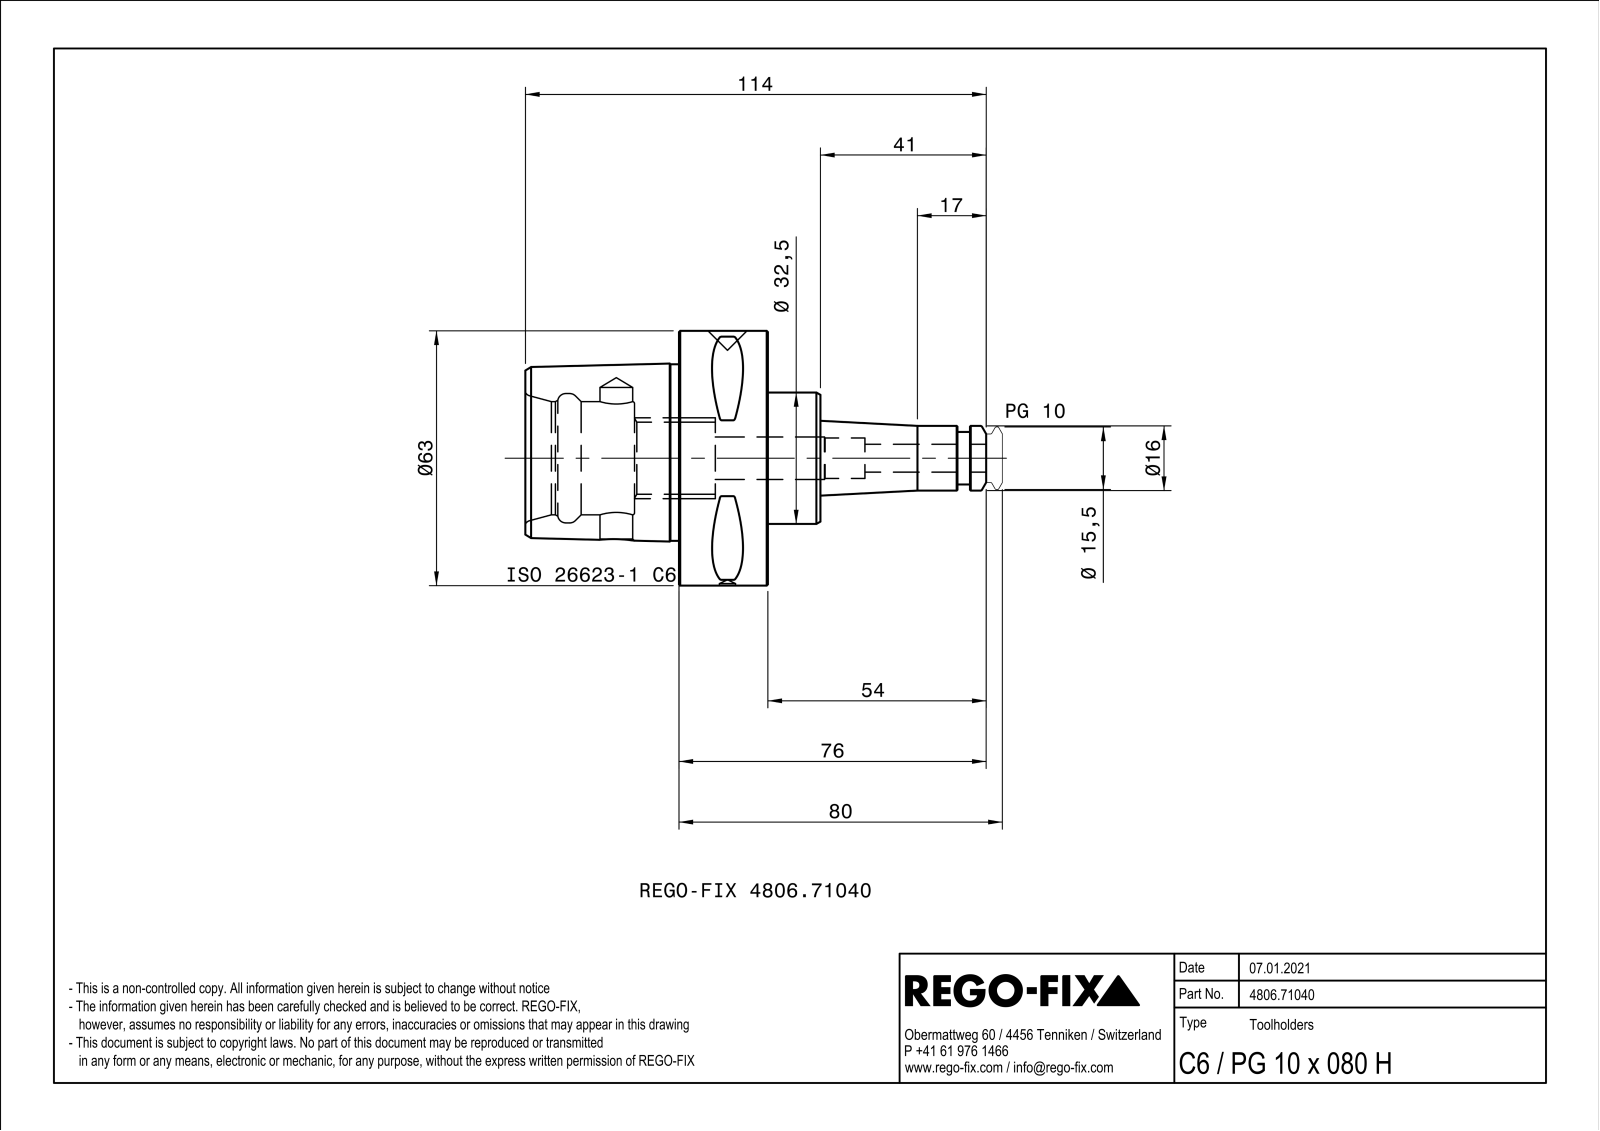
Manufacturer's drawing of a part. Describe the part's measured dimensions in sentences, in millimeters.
The part is named "NOCUT". Its 3-D file was written by "SIEMENS PLM Software Solid Edge ST10 (AUTOMOTIVE_DESIGN)". It is 1 solid with 135 faces: 25 planar, 27 cylindrical and 83 other. Overall it measures 114 by 63 by 63 millimeters. Its volume is 110 716 cubic millimeters and its surface area 25 093 square millimeters. Round holes: 1 of diameter 4, 1 of diameter 8.1, 1 of diameter 10, 1 of diameter 10.5, 1 of diameter 17.84, 1 of diameter 28, 1 of diameter 32. Round bosses or shafts: 1 of diameter 63, 1 of diameter 32.5, 1 of diameter 16, 1 of diameter 13. Partial cylindrical surfaces (rounded edges, fillets, slot ends): 8 of radius 0.5, 1 of radius 5. The main face-to-face distances are 22, 60, 38, 13, 35, 73, 24.89, 11, 46, 33. The hole center spacings are 27.5.
